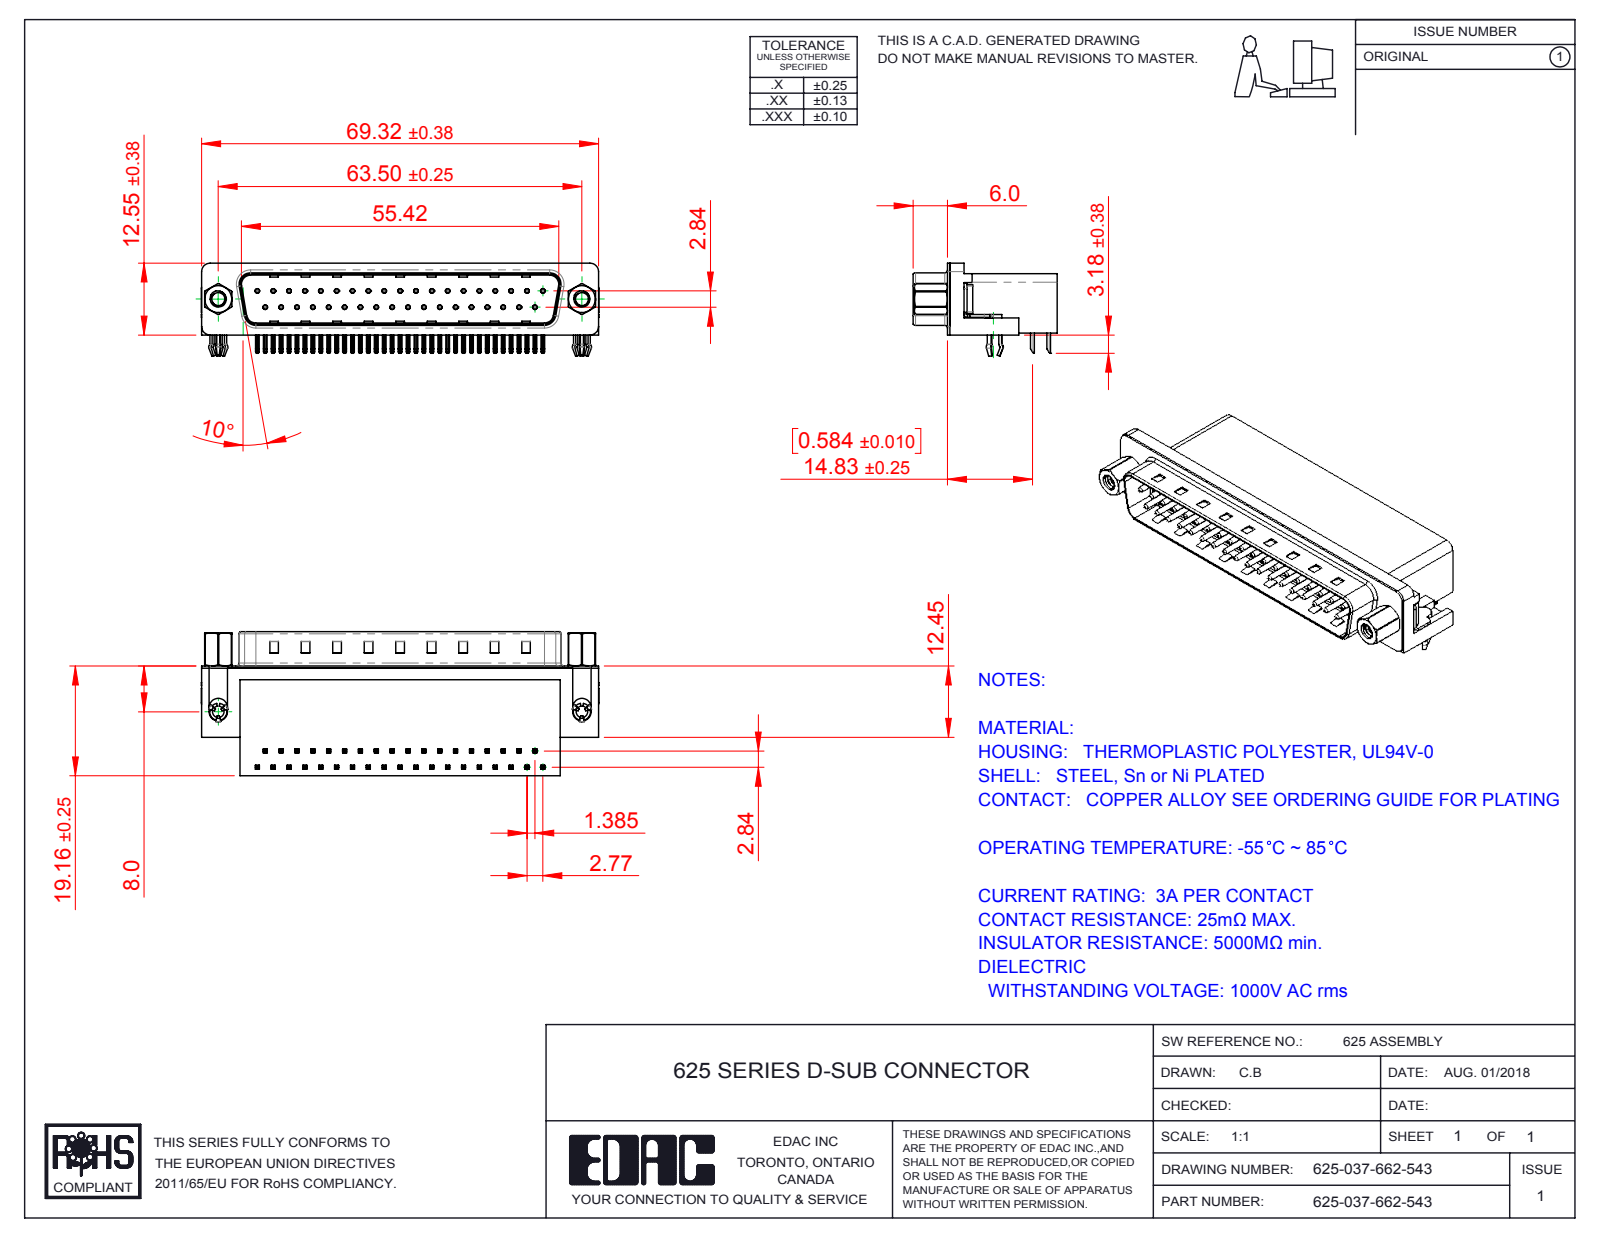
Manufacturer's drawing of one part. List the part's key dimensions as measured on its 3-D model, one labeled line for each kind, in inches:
Part name (STEP PRODUCT): 625 Shell_37 Socket; 625 4-40 Hex Standoff 5; 625 3 Prong Board Lock; 625-037-662-543 (+4 more)
STEP written by: SolidWorks 2016 (CONFIG_CONTROL_DESIGN)
Units: inches
Bodies: 45 solids, 3431 faces (2073 planar, 995 cylindrical, 363 other)
Overall size (bounding box): 2.732 × 0.991 × 0.64
Volume: 0.782 in³ · Surface area: 19.06 in²
Round holes (diameter × count): ⌀0.014 ×37, ⌀0.031 ×37, ⌀0.079 ×2, ⌀0.089 ×2, ⌀0.09 ×2, ⌀0.157 ×2, ⌀0.189 ×2, ⌀0.197 ×2
Round bosses / shafts (diameter × count): ⌀0.03 ×37, ⌀0.193 ×2, ⌀0.187 ×2, ⌀0.154 ×2, ⌀0.118 ×2, ⌀0.11 ×2
Partial cylindrical surfaces — rounded edges, fillets, slot ends (radius × count): R0.01 ×160, R0.005 ×74, R0.039 ×16, R0.02 ×9, R0.063 ×8, R0.059 ×7, R0.035 ×4, R0.079 ×4
Main face-to-face distances: 0.407, 0.016, 0.739, 0.345, 0.754, 0.398, 0.112, 0.082, 0.069, 0.329
Hole centre spacings: 0.124, 0.109, 0.218, 0.327, 0.436, 0.545, 0.763, 0.872
